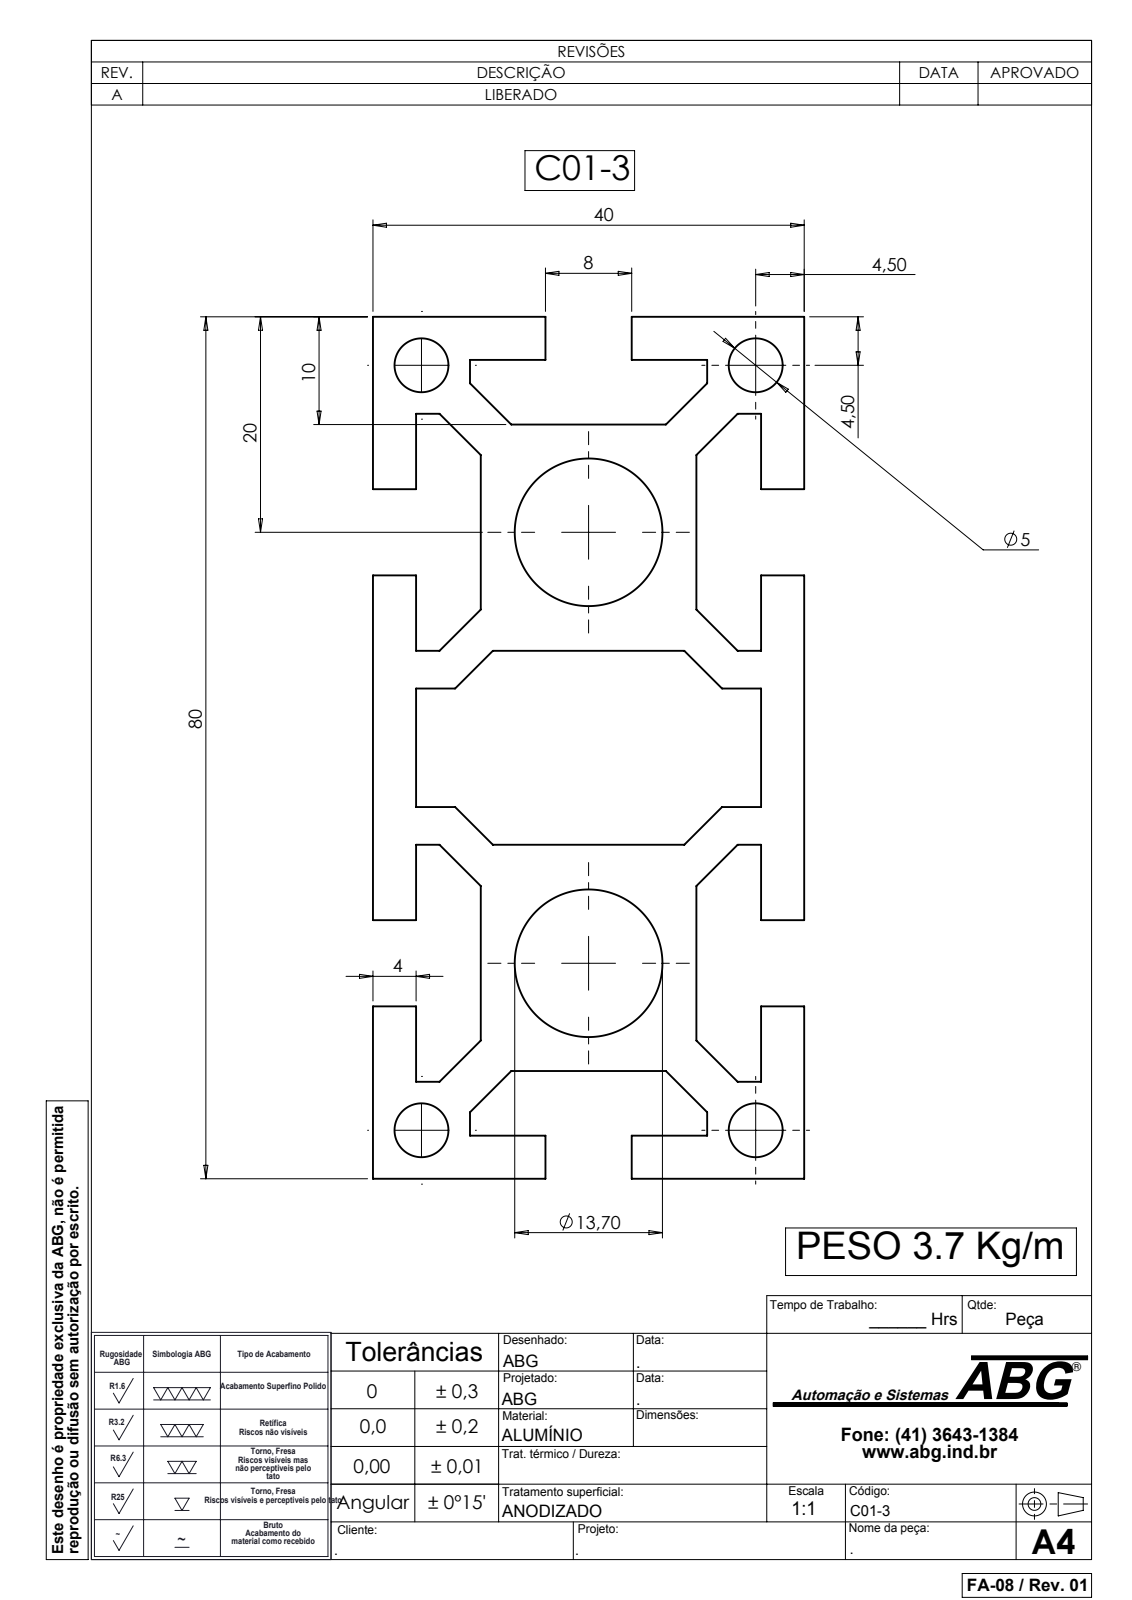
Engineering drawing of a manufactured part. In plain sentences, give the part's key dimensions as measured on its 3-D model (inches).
The part is named "C01-3". Its 3-D file was written by "SolidWorks 2007 (CONFIG_CONTROL_DESIGN)". It is 1 solid with 90 faces: 78 planar, 12 cylindrical and 0 other. Overall it measures 236.22 by 3.15 by 1.575 inches. Its volume is 523.5 cubic inches and its surface area 6 904 square inches. Round holes: 4 of diameter 0.197, 2 of diameter 0.539. The main face-to-face distances are 0.157, 0.236, 1.575, 0.394, 1.417, 0.787, 1.181, 1.024, 1.22, 1.26. The hole center spacings are 0.863, 2.269, 1.22, 2.795, 3.05, 1.575.
